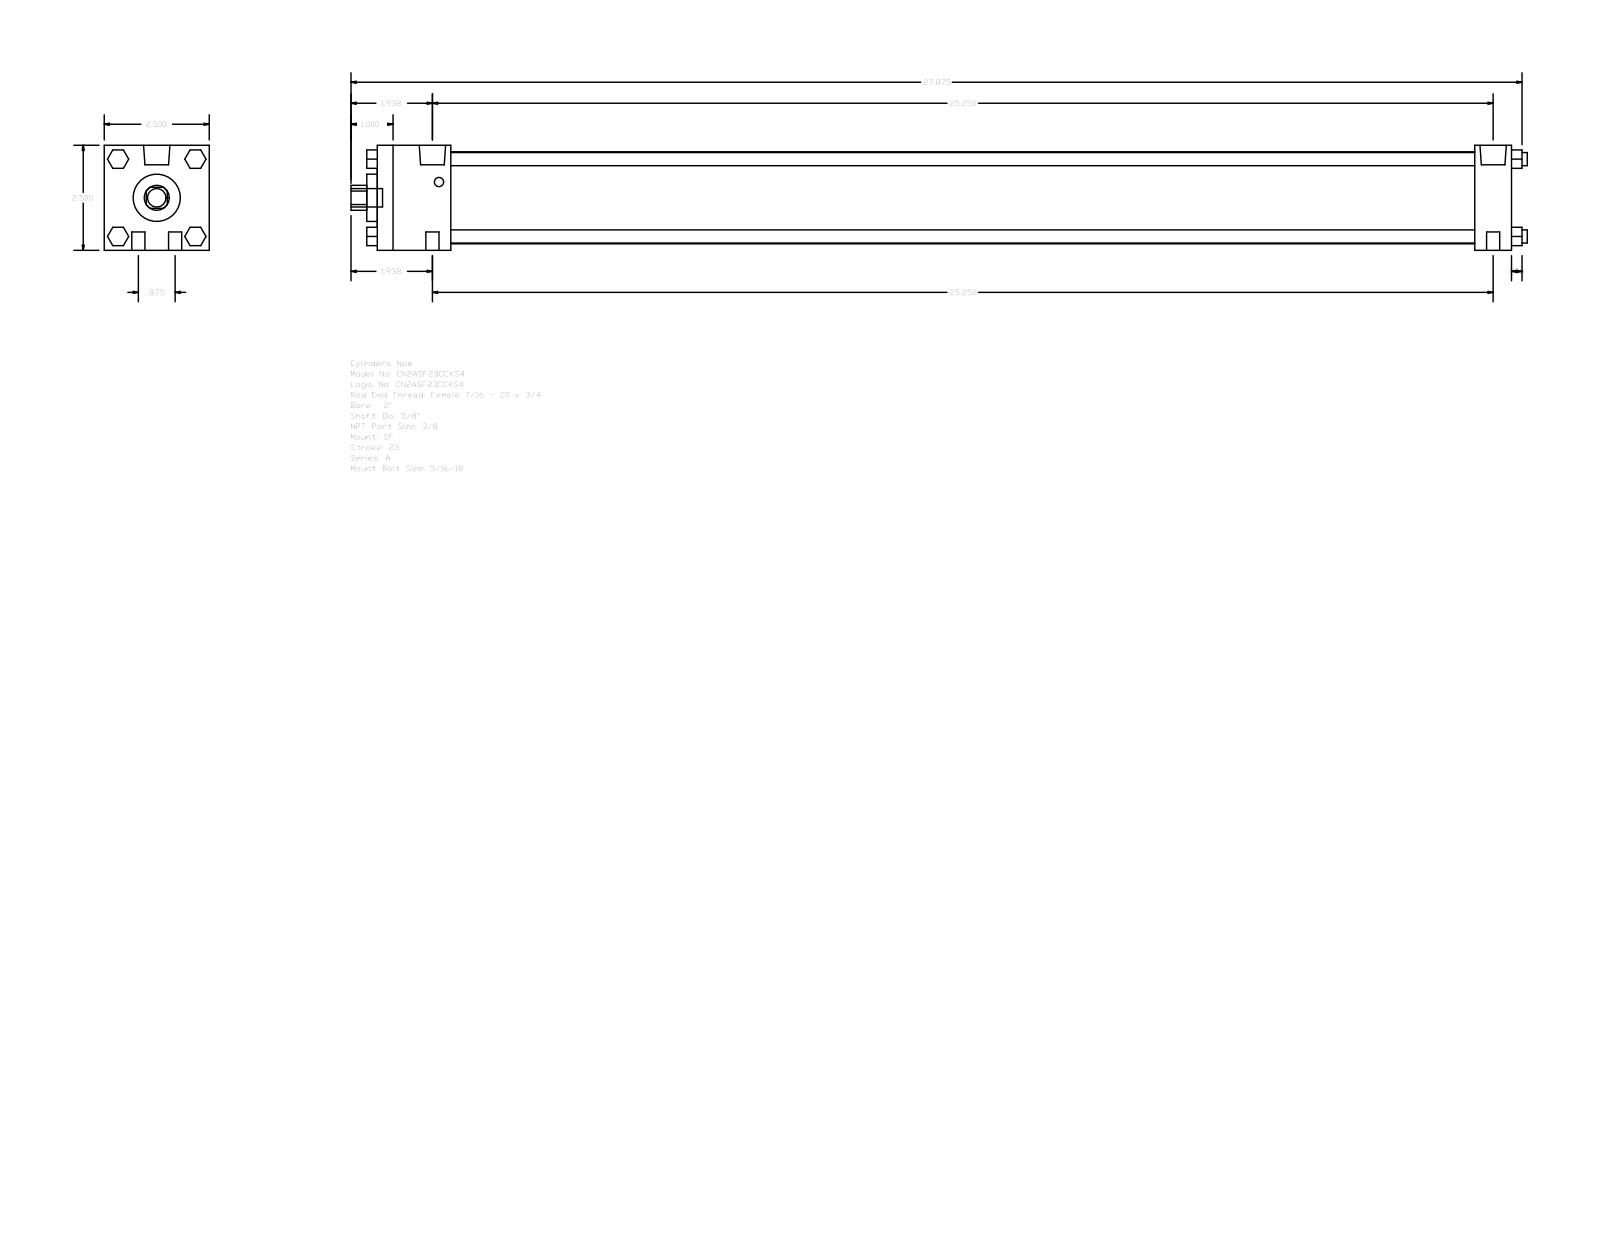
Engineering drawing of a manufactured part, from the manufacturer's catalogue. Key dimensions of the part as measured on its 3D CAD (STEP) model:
Part name (STEP PRODUCT): A_SF__0200_0.625
STEP written by: GSSL Pune (CONFIG_CONTROL_DESIGN)
Units: millimetres
Bodies: 0 solids, 124 faces (94 planar, 30 cylindrical, 0 other)
Overall size (bounding box): 711.2 × 63.5 × 63.5
Round holes (diameter × count): ⌀15.88 ×1, ⌀28.57 ×1, ⌀55.63 ×1
Round bosses / shafts (diameter × count): ⌀7.94 ×8, ⌀15.93 ×2, ⌀5.56 ×2, ⌀11.11 ×1
Partial cylindrical surfaces — rounded edges, fillets, slot ends (radius × count): R7.54 ×1
Main face-to-face distances: 63.5, 685.79, 663.57, 22.22, 44.45, 619.12, 641.34, 6.35, 692.14, 50.8
